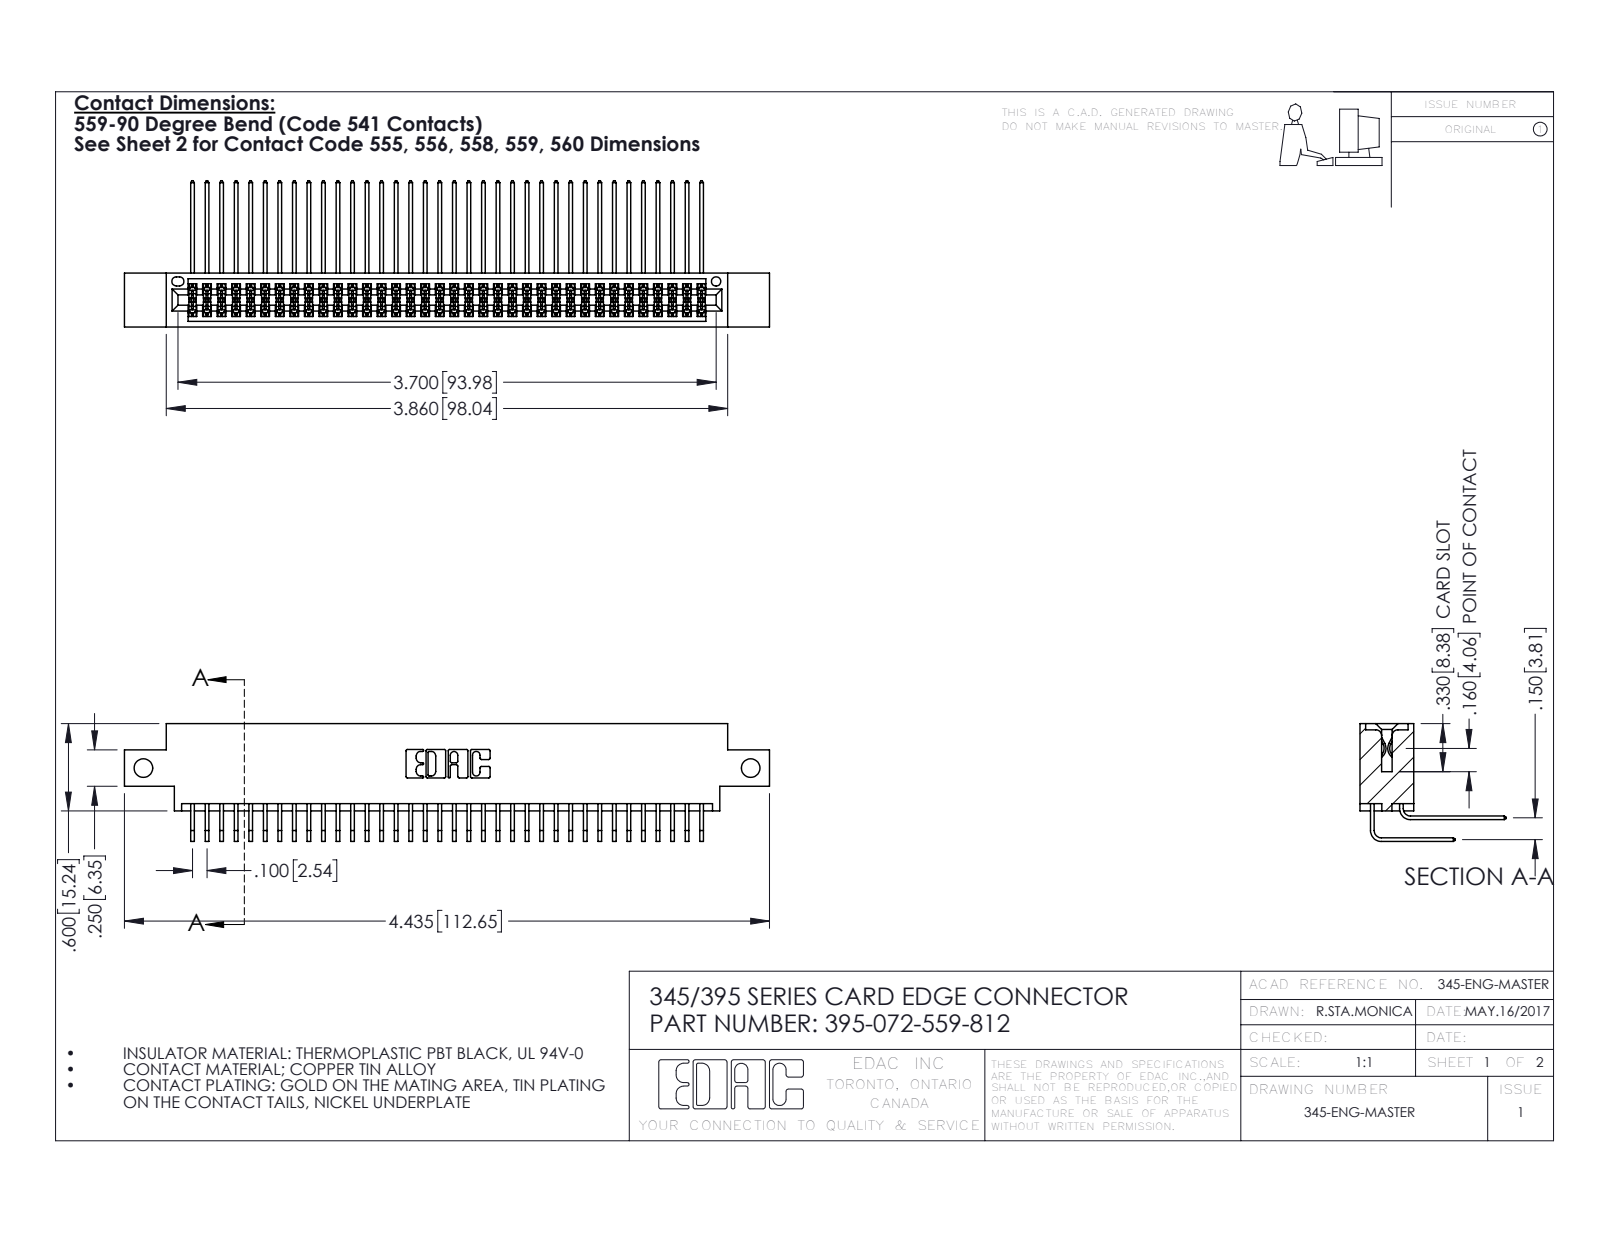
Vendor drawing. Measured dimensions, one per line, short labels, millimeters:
name: 395-072-559-812; 345-292-001_559 Tail - 2; 345 Part_0.170 Offset - Side Mount; 345-292-001_558 559 Tail - 1
written by: SolidWorks 2016 (CONFIG_CONTROL_DESIGN)
unit: mm
bodies: 73 solids, 3874 faces (2604 planar, 1270 cylindrical, 0 other)
size: 112.6 × 25.5 × 20.5
volume: 11 100 mm³; area: 18 260 mm²
holes: 2× ⌀3.3, 1× ⌀1.6
rounds: 108× R0.2, 22× R0.3, 6× R0.2, 6× R0.8, 3× R0.7, 2× R0.4, 2× R0.5, 2× R0.6
face distances: 1.8, 7.6, 9.4, 5.1, 2.5, 6.9, 0.6, 5.7, 4.4, 3.8
hole spacings: 106
